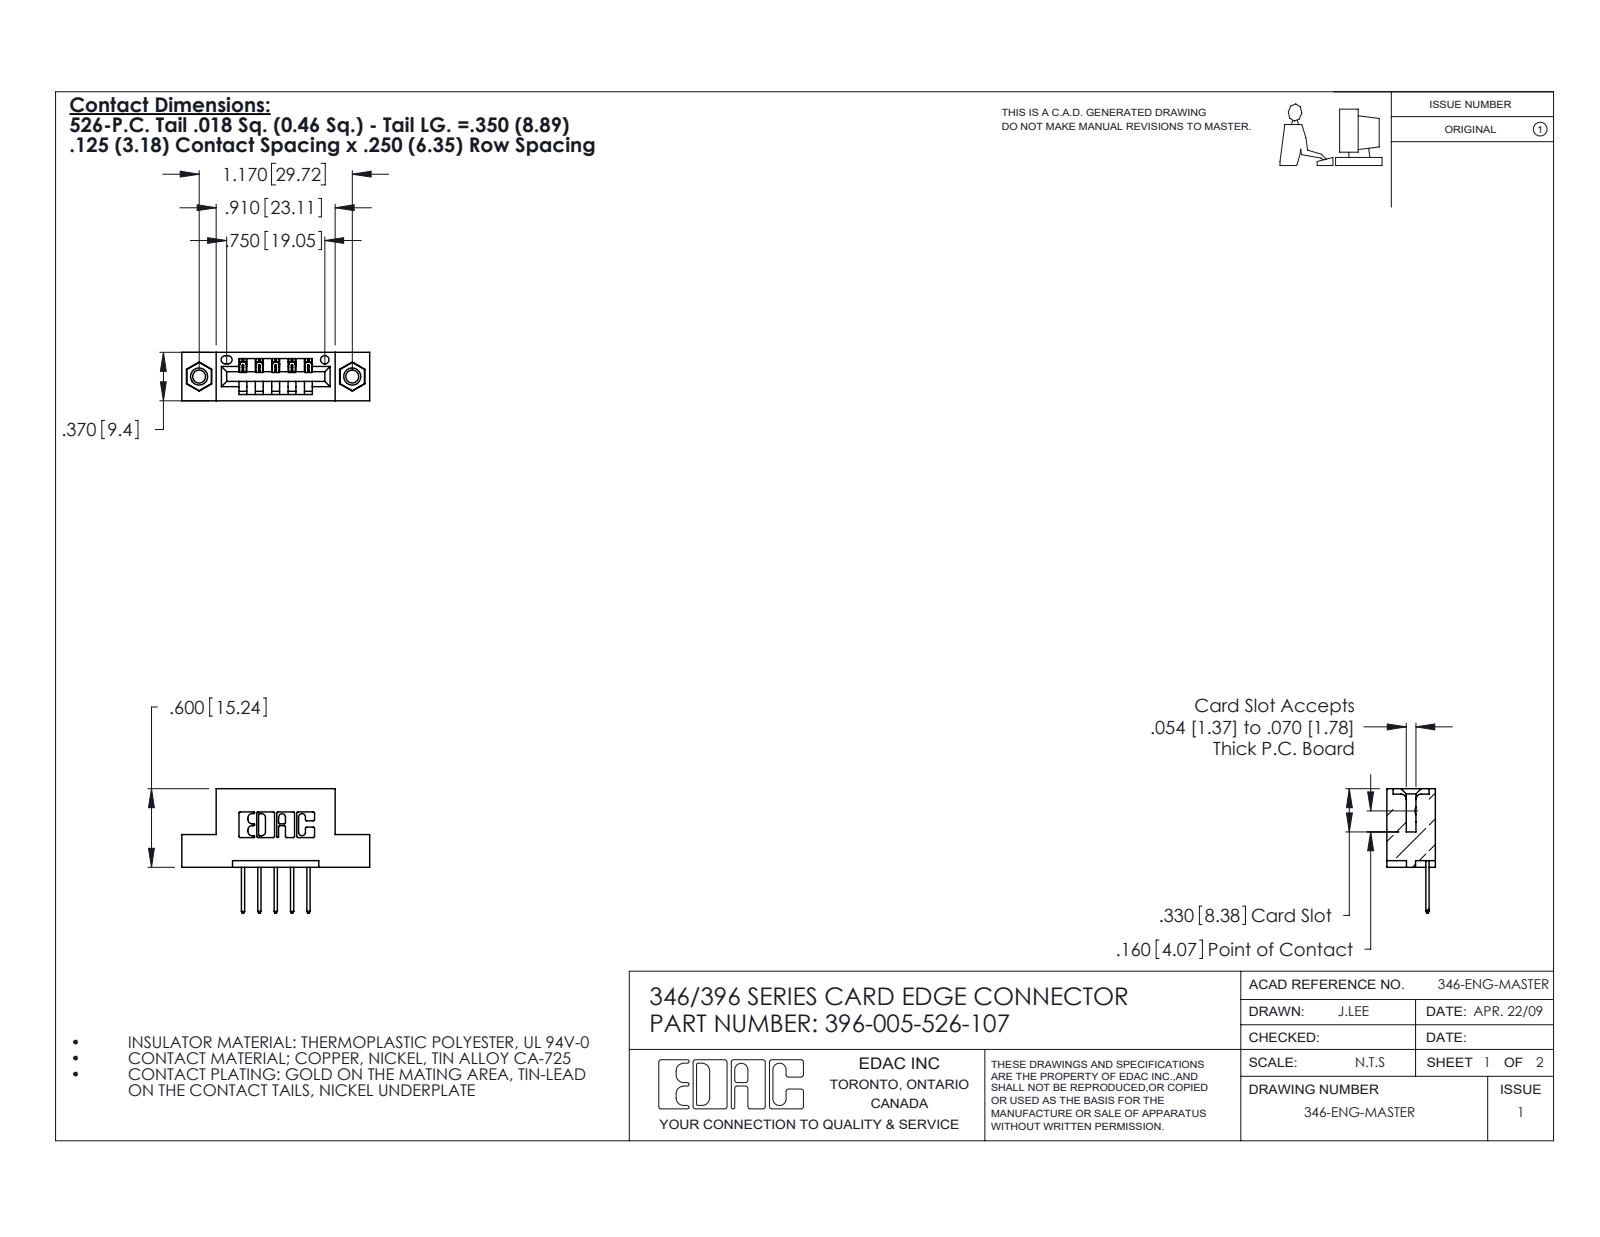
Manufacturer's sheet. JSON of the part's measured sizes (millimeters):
{"part_name": "396-005-526-107; 345-292-001_345-293-126; 346 Part_Flush Mounting Lugs - 0.156 Dia-TI; 345-250-001_345-250-005-103", "step_written_by": "SolidWorks 2020 (CONFIG_CONTROL_DESIGN)", "units": "millimeters", "bodies": {"solids": 8, "faces": 472, "planar": 308, "cylindrical": 148, "other": 16}, "overall_size": [36.4, 24.1, 9.4], "volume_mm3": 3210, "surface_area_mm2": 3651, "round_holes": [[2.5, 2], [3.2, 2], [4, 2], [1.6, 1]], "round_bosses_or_shafts": [[3.9, 2]], "partial_cylinders_radius": [[0.3, 22], [0.2, 10], [0.3, 10], [0.2, 6], [0.8, 6], [0.7, 3], [0.8, 2], [1, 2]], "face_to_face_distances": [6.4, 9.4, 1.2, 8.2, 14, 3.8, 5.6, 2.5, 4.4, 3.2], "hole_center_spacings": [6.2, 24.6, 29.7]}
